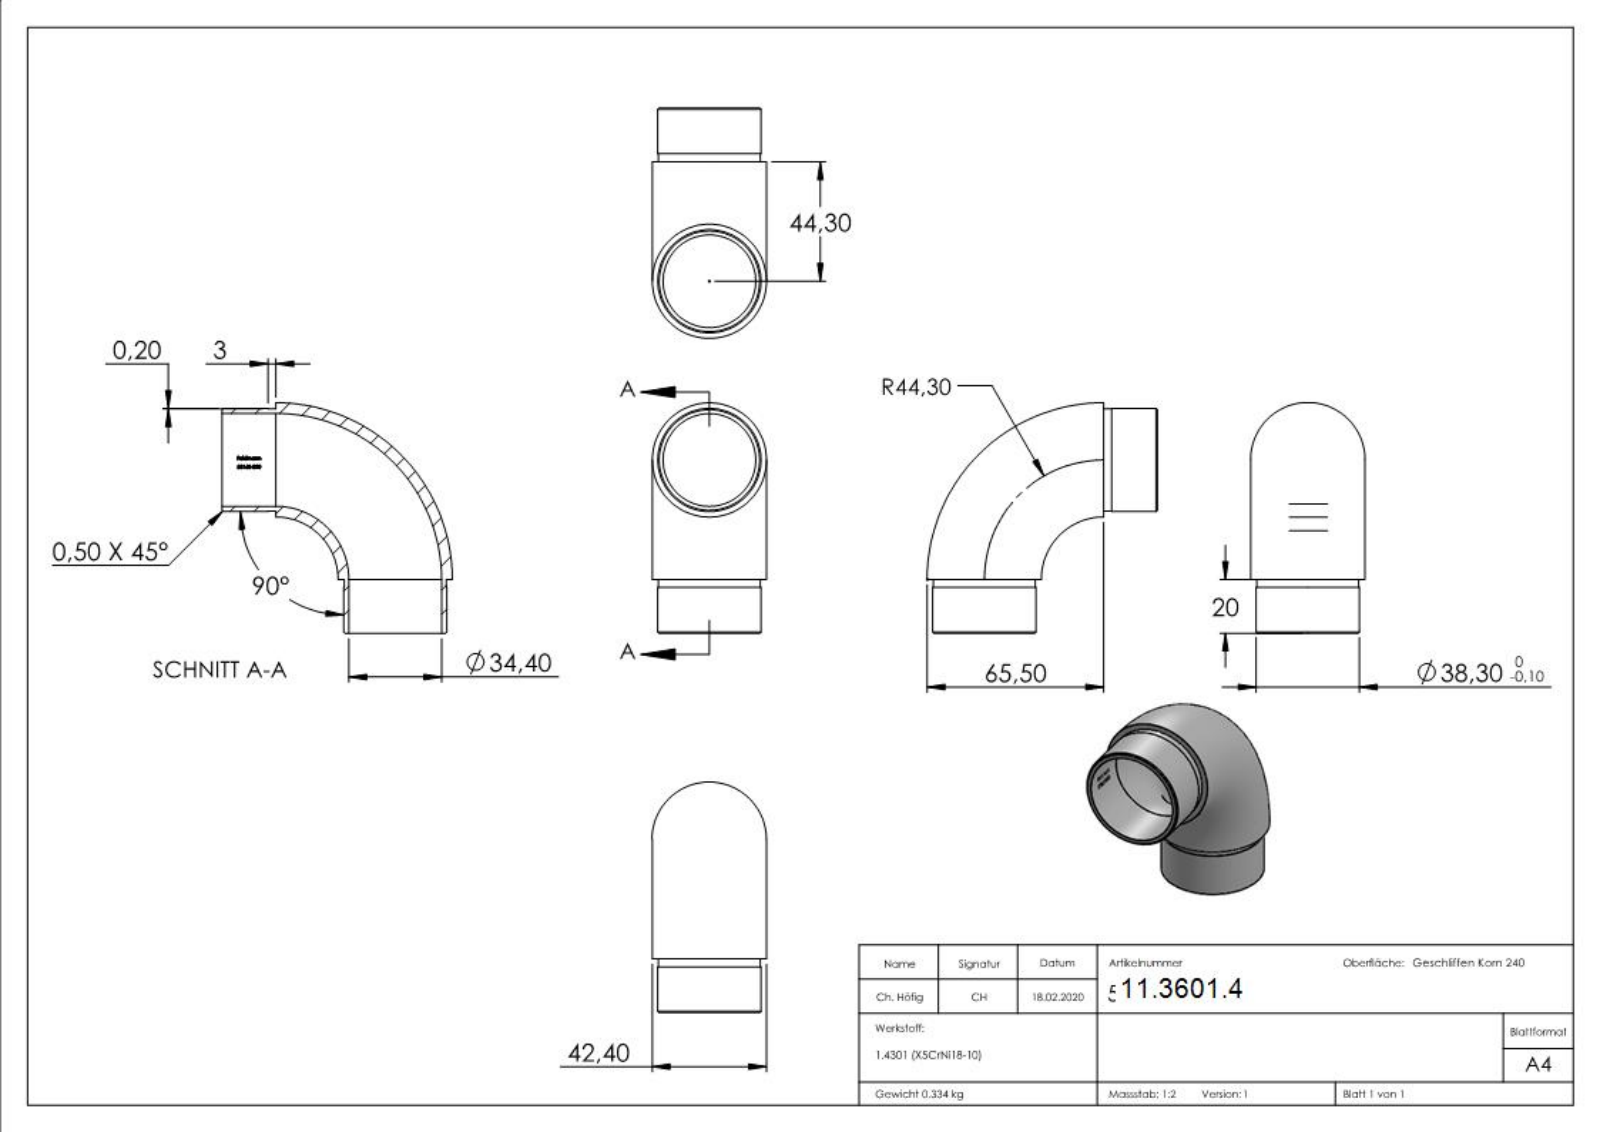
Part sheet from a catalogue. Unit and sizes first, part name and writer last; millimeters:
Units: millimetres
Overall size (bounding box): 85.5 × 85.5 × 42.4
Round holes (diameter × count): ⌀34.4 ×2
Round bosses / shafts (diameter × count): ⌀38.3 ×2, ⌀37.9 ×2
Partial cylindrical surfaces — rounded edges, fillets, slot ends (radius × count): R17.3 ×1
Main face-to-face distances: 20, 17, 3, 0.39, 1.26, 2.97, 4.23, 1.32, 3.66, 3.27
Volume: 42 312 mm³ · Surface area: 26 917 mm²
Bodies: 1 solid, 237 faces (91 planar, 30 cylindrical, 116 other)
Part name (STEP PRODUCT): 56160-320
STEP written by: SolidWorks 2015 (CONFIG_CONTROL_DESIGN)
